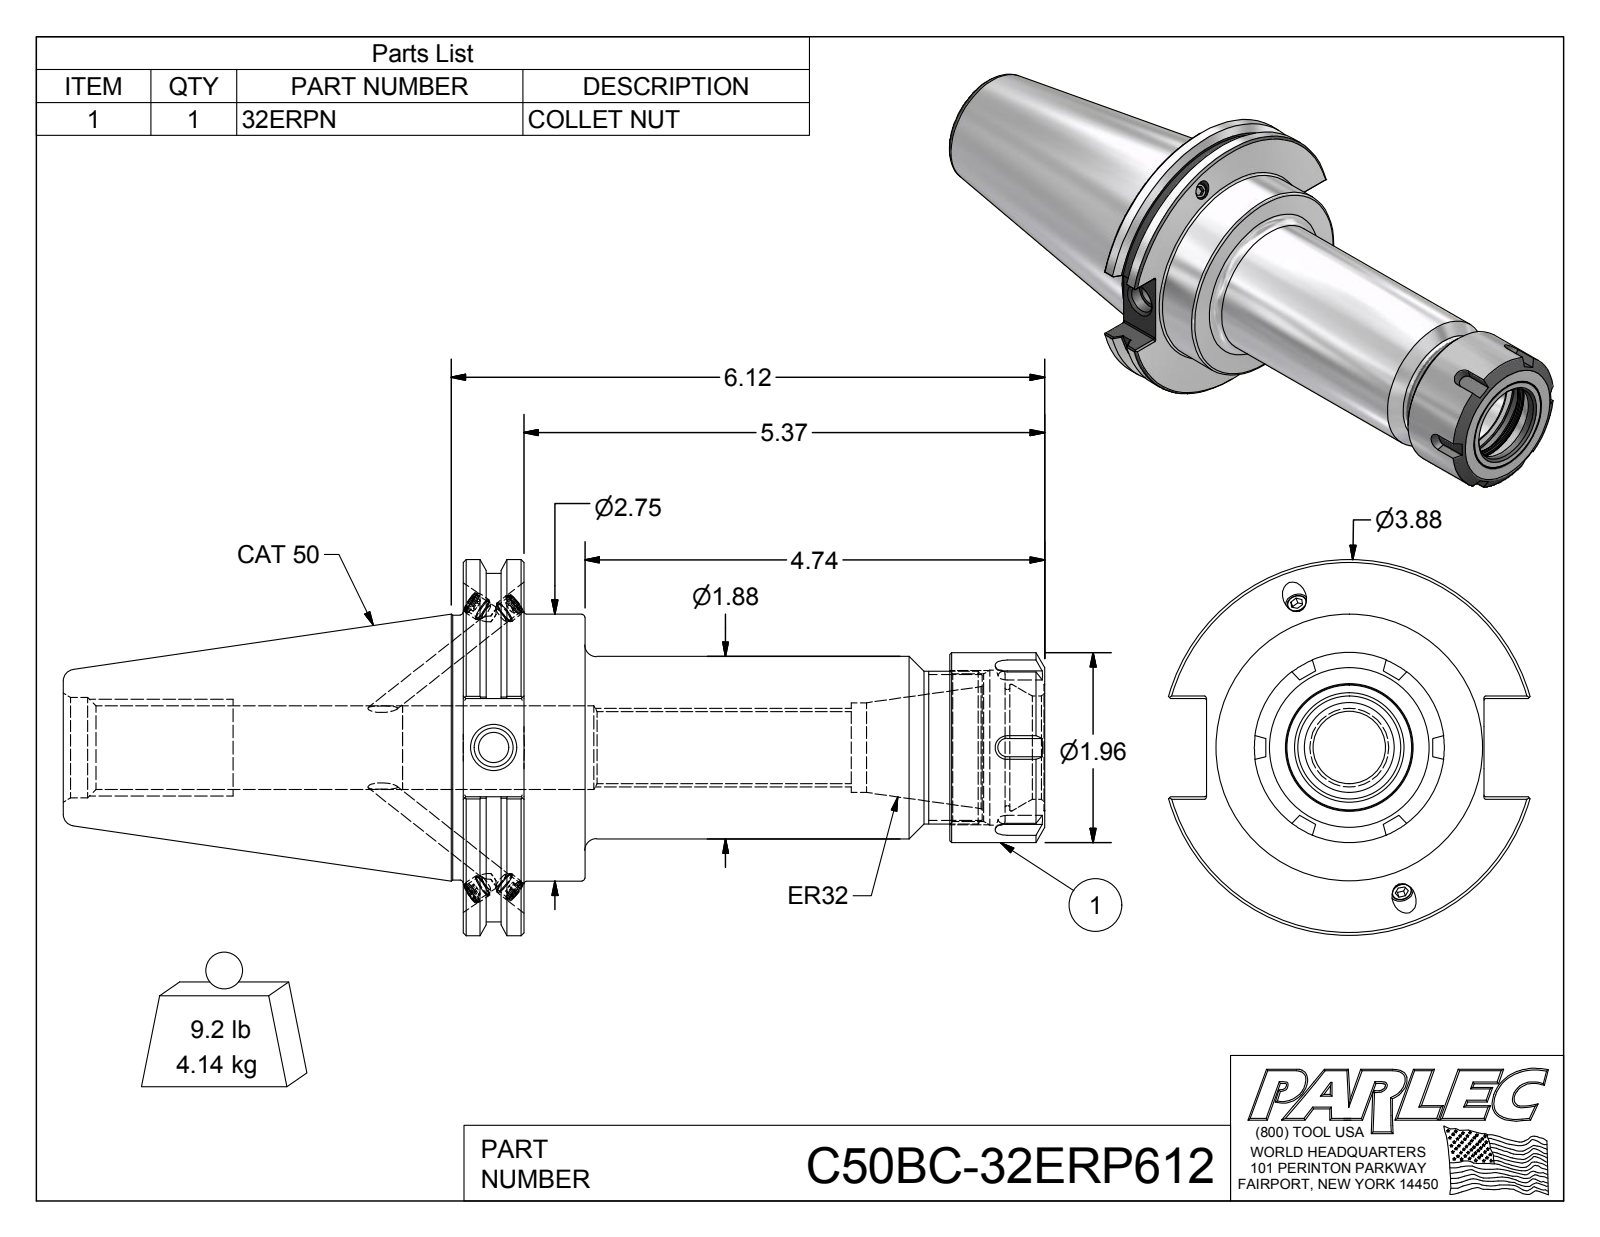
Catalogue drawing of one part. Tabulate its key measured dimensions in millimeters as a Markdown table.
| quantity | value |
| --- | --- |
| part name | C50BC-32ERP612; C50BCB-32ER6-1; 029-966; 32ERPN |
| STEP written by | Autodesk Inventor 2012 (AUTOMOTIVE_DESIGN) |
| units | millimeters |
| bodies | 6 solids, 223 faces (100 planar, 55 cylindrical, 68 other) |
| overall size | 257 × 98.4 × 94.7 |
| volume | 530 000 mm³ |
| surface area | 81 480 mm² |
| round holes (diameter × count) | 5 × 4, 6.1 × 4, 8 × 1, 10.1 × 1, 18.9 × 1, 22 × 1, 22 × 1, 23.5 × 1, 26.4 × 1, 27 × 1, 30.5 × 1, 33.1 × 1 |
| round bosses / shafts (diameter × count) | 6.2 × 4, 6 × 4, 98.4 × 1, 91.3 × 1, 69.9 × 1, 69.3 × 1, 49.7 × 1, 47.8 × 1 |
| partial cylindrical surfaces (radius × count) | 0.5 × 12 |
| main face-to-face distances | 15.9, 31.9, 16, 152.3, 136.4, 120.4, 127.4, 111.6, 95.6, 24.8 |
